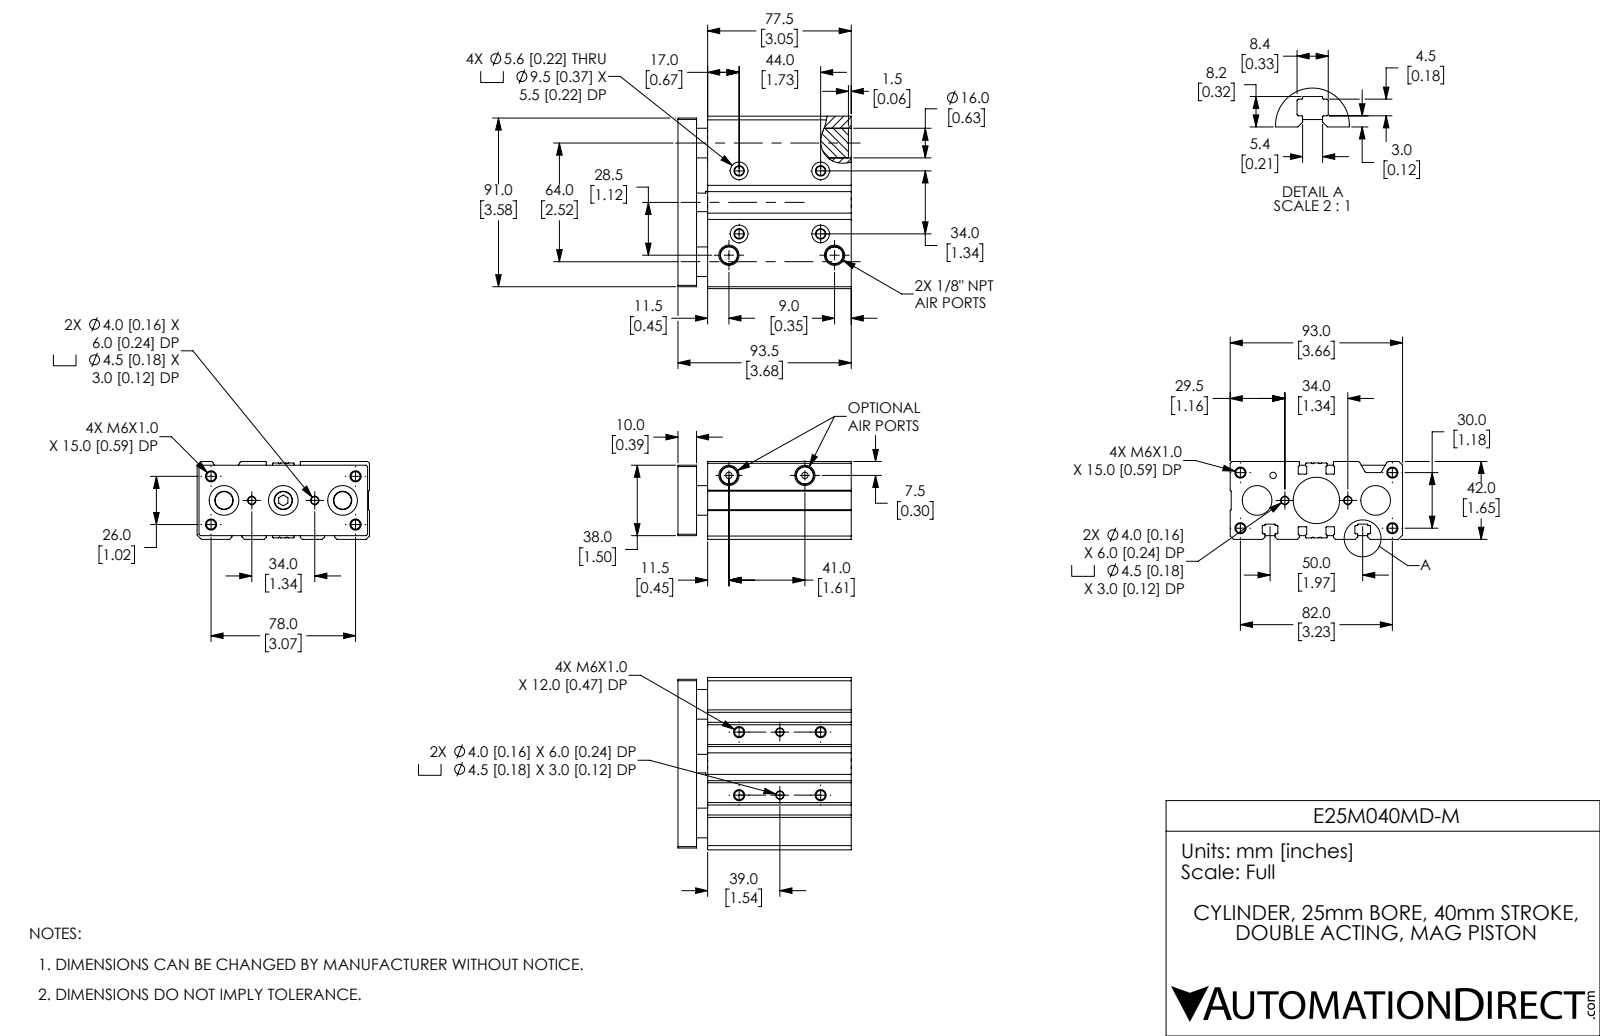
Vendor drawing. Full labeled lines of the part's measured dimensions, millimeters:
Part name (STEP PRODUCT): E25M040MD-M; E25M040MD-M_BODY; E25M040MD-M_ENDPLATE
STEP written by: SolidWorks 2019 (CONFIG_CONTROL_DESIGN)
Units: millimetres
Bodies: 5 solids, 423 faces (139 planar, 190 cylindrical, 94 other)
Overall size (bounding box): 93.5 × 93 × 42
Volume: 285 862 mm³ · Surface area: 80 812 mm²
Round holes (diameter × count): ⌀4.92 ×8, ⌀4 ×4, ⌀4.5 ×4, ⌀4.92 ×4, ⌀5.6 ×4, ⌀9.5 ×4, ⌀3.43 ×3, ⌀8 ×3, ⌀16 ×3, ⌀9.91 ×2, ⌀16 ×1, ⌀25 ×1
Round bosses / shafts (diameter × count): ⌀12 ×1, ⌀9.91 ×1
Partial cylindrical surfaces — rounded edges, fillets, slot ends (radius × count): R0.2 ×32, R0.4 ×28, R1 ×4, R0.3 ×2
Main face-to-face distances: 6, 42, 16, 10, 2, 93.5, 83.5, 77.5, 40, 93
Hole centre spacings: 2.83, 14.76, 17.49, 22, 25.55, 28.07, 28.3, 34
